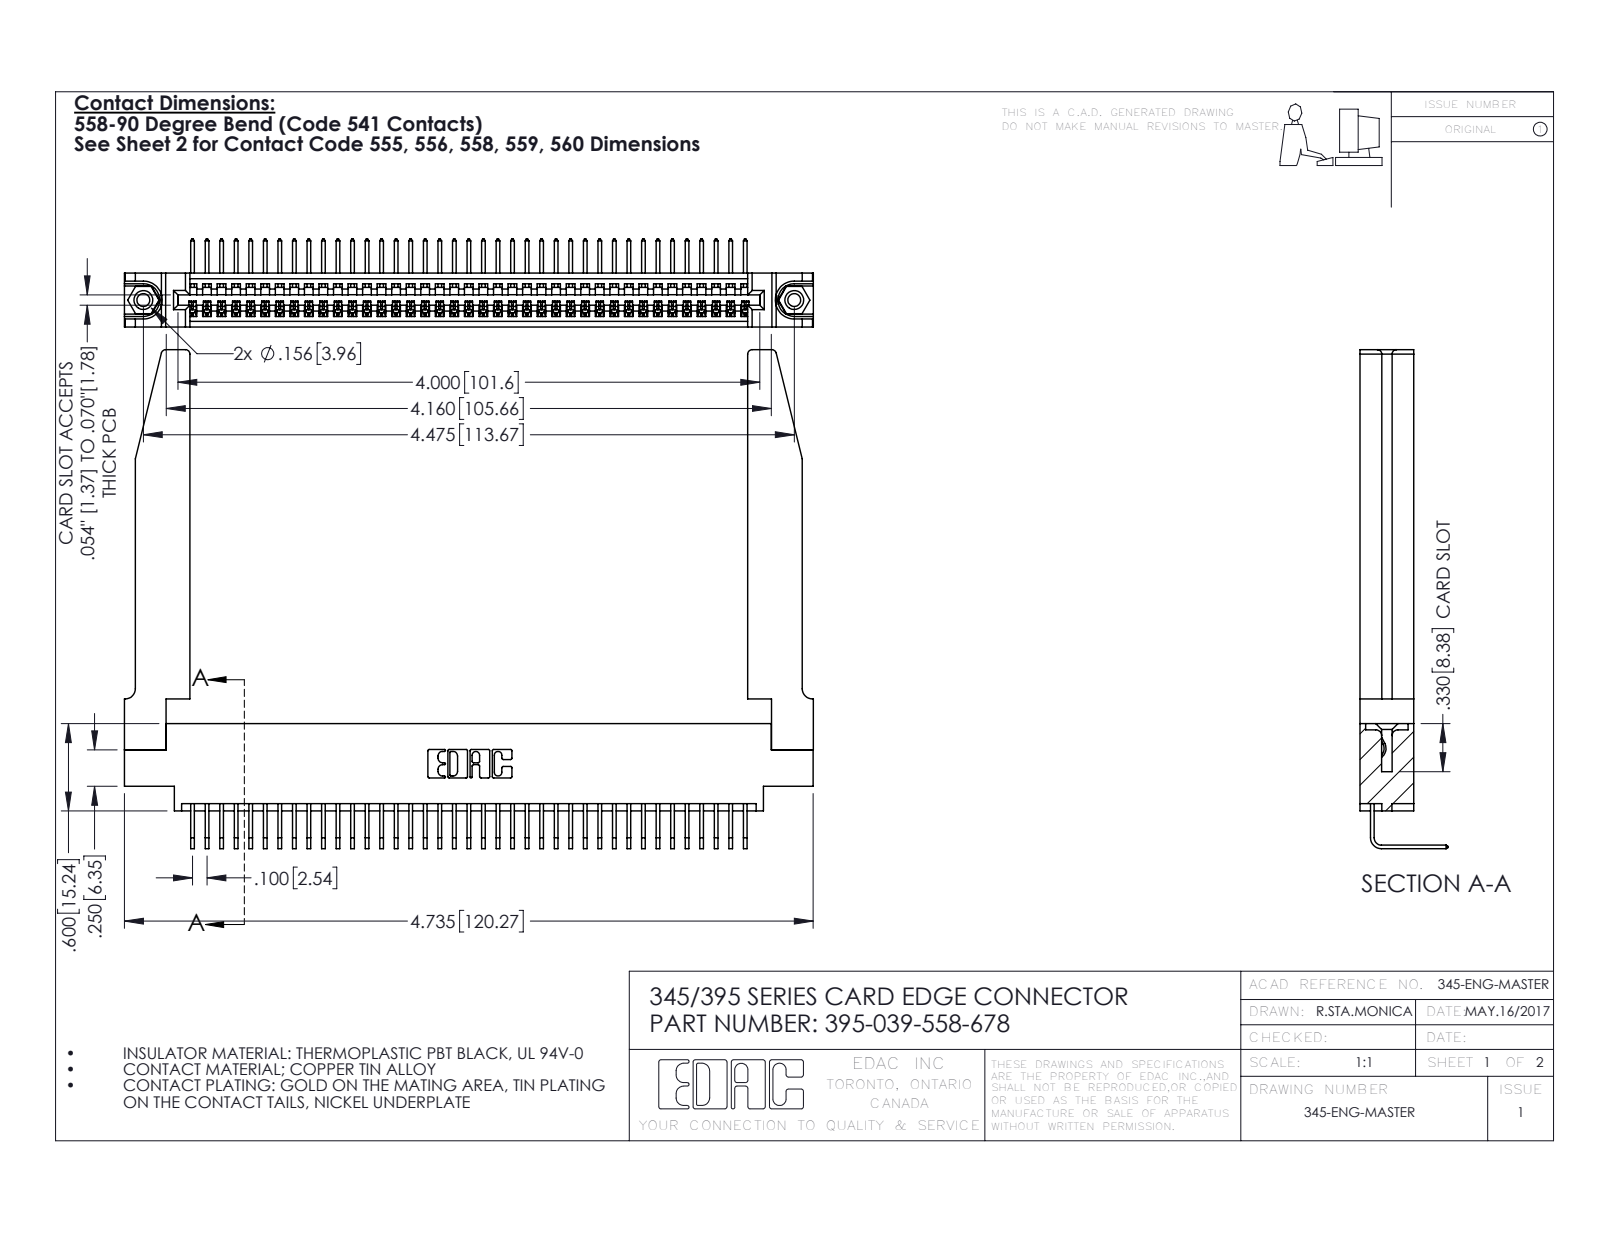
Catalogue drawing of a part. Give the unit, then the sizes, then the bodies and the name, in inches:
Units: inches
Overall size (bounding box): 4.736 × 3.429 × 0.605
Round holes (diameter × count): ⌀0.089 ×2, ⌀0.125 ×2, ⌀0.156 ×2, ⌀0.064 ×1
Round bosses / shafts (diameter × count): ⌀0.155 ×2
Partial cylindrical surfaces — rounded edges, fillets, slot ends (radius × count): R0.006 ×78, R0.01 ×22, R0.03 ×8, R0.007 ×6, R0.031 ×6, R0.026 ×3, R0.031 ×2, R0.04 ×2
Main face-to-face distances: 0.37, 0.072, 0.298, 0.2, 0.098, 0.272, 0.025, 0.225, 0.148, 0.15
Hole centre spacings: 0.27, 4.239, 4.475
Volume: 1.171 in³ · Surface area: 35.45 in²
Bodies: 44 solids, 2704 faces (1864 planar, 788 cylindrical, 52 other)
Part name (STEP PRODUCT): 345 Part_0.170 Offset - 0.156 Dia-TH; 345-250-001_345-250-001-102; 345-292-001_558 Tail - 2; 345-220-078_345-220-078 (+1 more)
STEP written by: SolidWorks 2016 (CONFIG_CONTROL_DESIGN)
